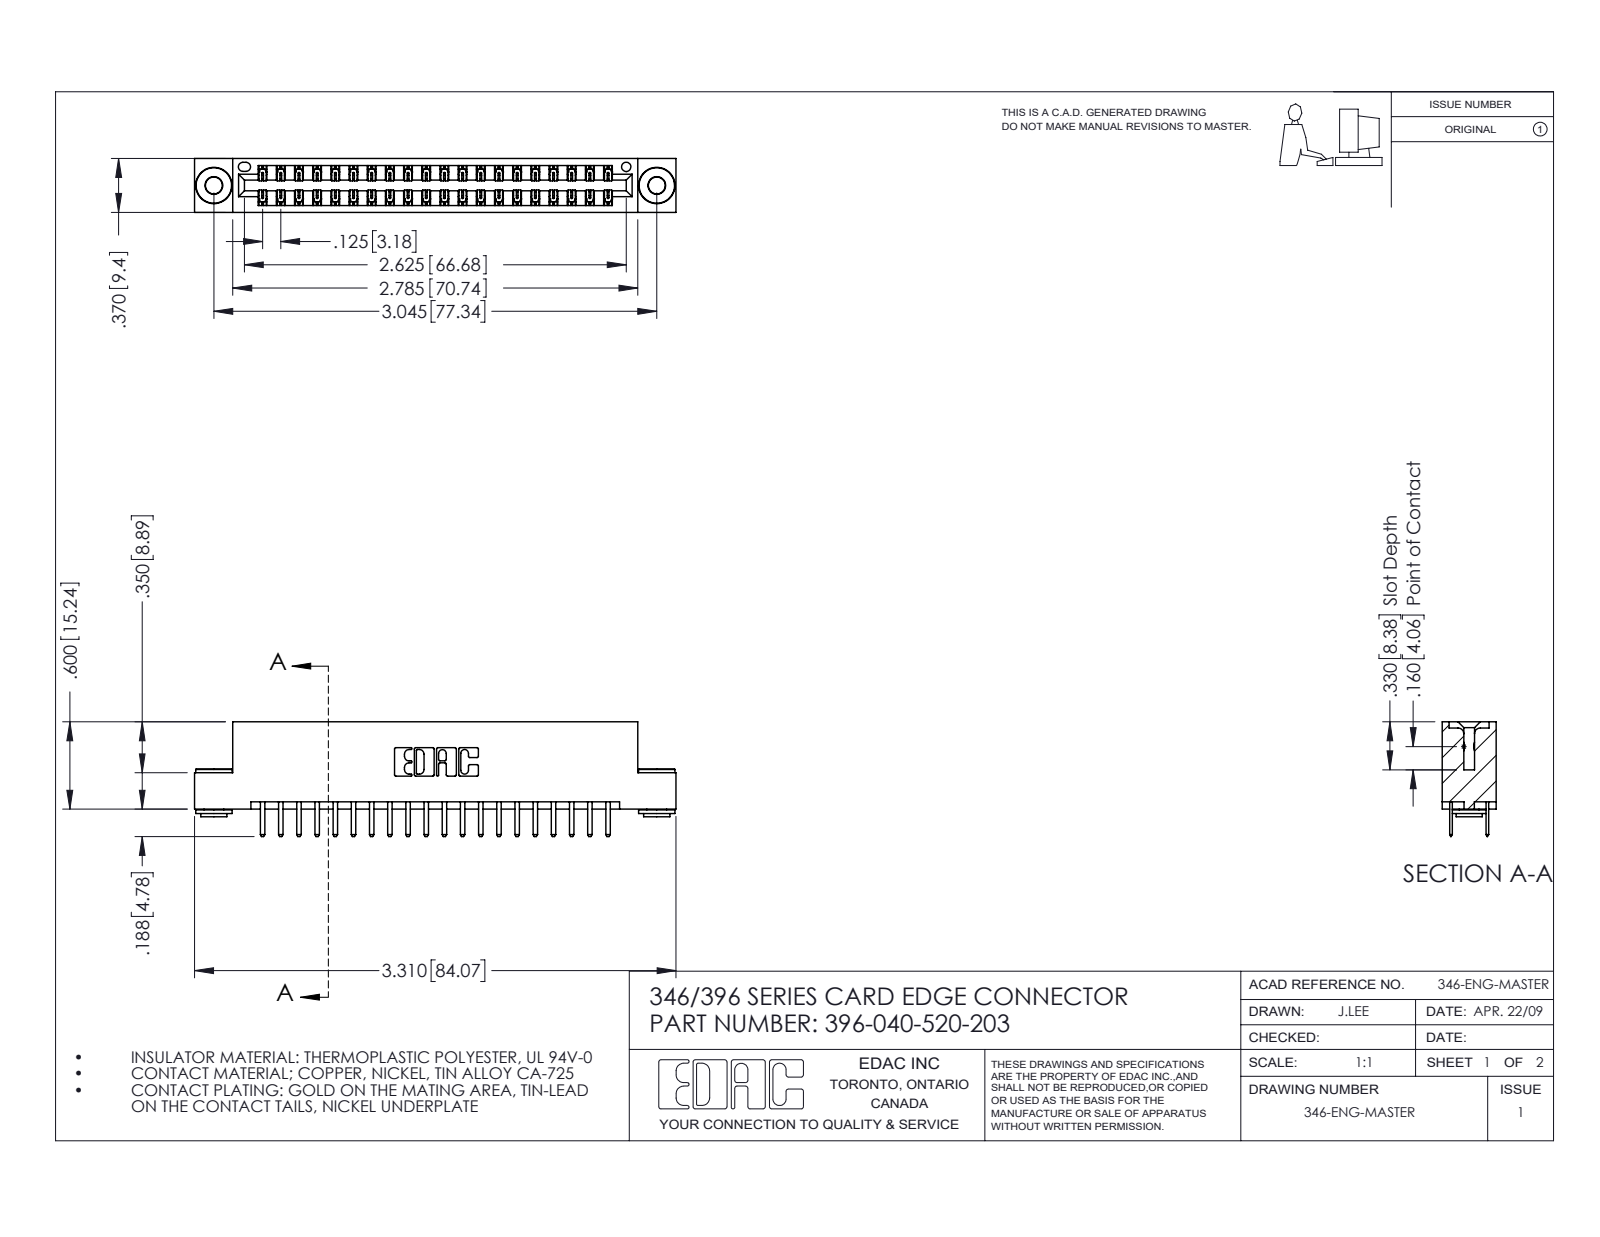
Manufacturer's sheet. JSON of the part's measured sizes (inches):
{"part_name": "345-250-002_345-250-002-102; 345-292-001_345-293-120; 396-040-520-203; 346 Part_Flush Mounting Lugs - 0.156 Dia-TH", "step_written_by": "SolidWorks 2016 (CONFIG_CONTROL_DESIGN)", "units": "inches", "bodies": {"solids": 43, "faces": 2400, "planar": 1566, "cylindrical": 826, "other": 8}, "overall_size": [3.31, 0.788, 0.37], "volume_in3": 0.49, "surface_area_in2": 16.84, "round_holes": [[0.116, 2], [0.156, 2], [0.064, 1]], "round_bosses_or_shafts": [[0.25, 2], [0.18, 2], [0.136, 2]], "partial_cylinders_radius": [[0.006, 60], [0.01, 44], [0.01, 22], [0.007, 6], [0.031, 6], [0.026, 3], [0.014, 2], [0.022, 2]], "face_to_face_distances": [0.25, 0.048, 0.322, 0.37, 0.025, 0.275, 0.072, 0.298, 0.148, 0.222], "hole_center_spacings": [0.246, 2.837, 3.045]}
